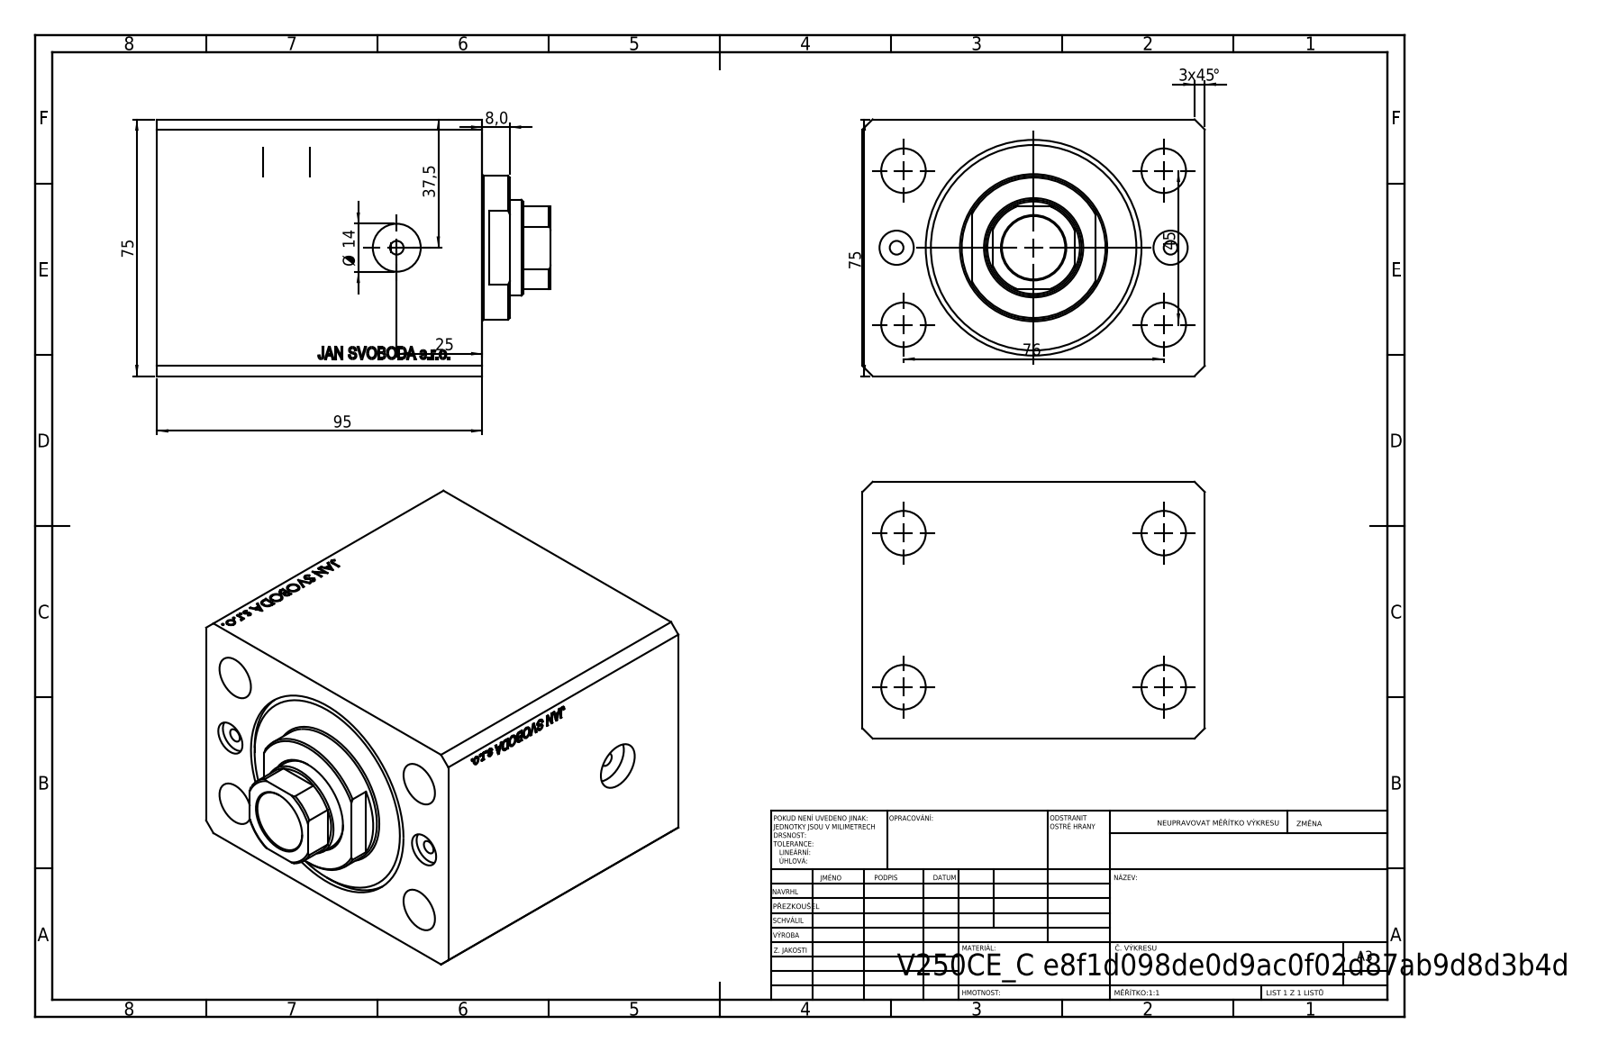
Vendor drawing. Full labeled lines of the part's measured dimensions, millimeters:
Part name (STEP PRODUCT): V250CE_C_Body; V250CE_VC_C; V250CE_C_VCP
STEP written by: SolidWorks 2019 (CONFIG_CONTROL_DESIGN)
Units: millimetres
Bodies: 3 solids, 864 faces (428 planar, 44 cylindrical, 392 other)
Overall size (bounding box): 114.9 × 100 × 75
Volume: 637 680 mm³ · Surface area: 109 976 mm²
Round holes (diameter × count): ⌀4 ×4, ⌀13 ×4, ⌀10 ×2, ⌀14 ×2, ⌀18.5 ×1, ⌀28 ×1, ⌀50 ×1, ⌀63 ×1
Round bosses / shafts (diameter × count): ⌀42 ×1
Partial cylindrical surfaces — rounded edges, fillets, slot ends (radius × count): R13.5 ×1
Main face-to-face distances: 75, 100, 95, 11.9, 83.1, 68.4, 56.5, 26.6, 20, 48.4
Hole centre spacings: 22.59, 44.16, 81.18, 45, 40, 76, 88.32, 80
